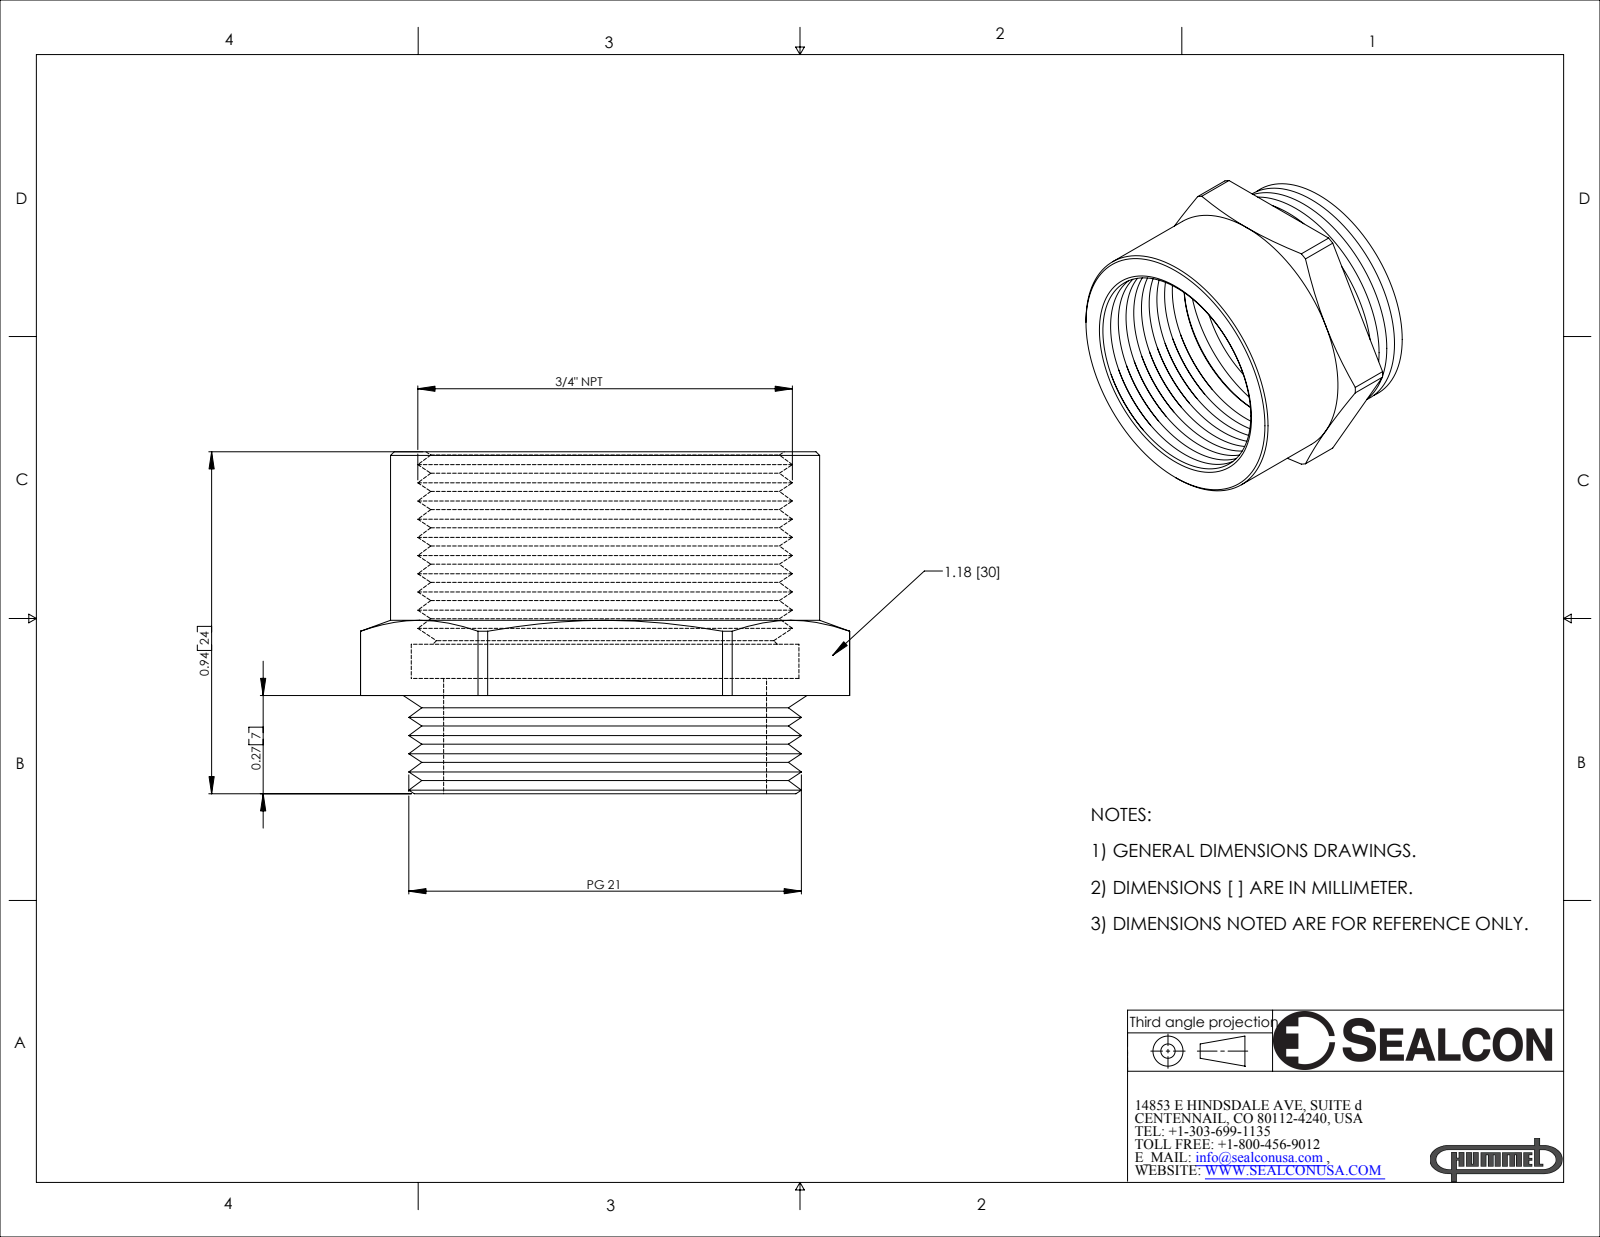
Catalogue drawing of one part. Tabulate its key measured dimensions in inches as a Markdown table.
| quantity | value |
| --- | --- |
| part name | AG-2134-BR |
| STEP written by | SolidWorks 2007 (CONFIG_CONTROL_DESIGN) |
| units | inches |
| bodies | 1 solid, 99 faces (11 planar, 13 cylindrical, 75 other) |
| overall size | 1.345 × 1.18 × 0.94 |
| volume | 0.298 in³ |
| surface area | 9.502 in² |
| round holes (diameter × count) | 0.888 × 1, 1.066 × 1 |
| round bosses / shafts (diameter × count) | 1.18 × 1 |
| partial cylindrical surfaces (radius × count) | 0.673 × 1 |
| main face-to-face distances | 1.18, 0.623, 0.317, 0.94, 0.27, 0.047, 0.67, 0.411, 0.141, 0.094 |
